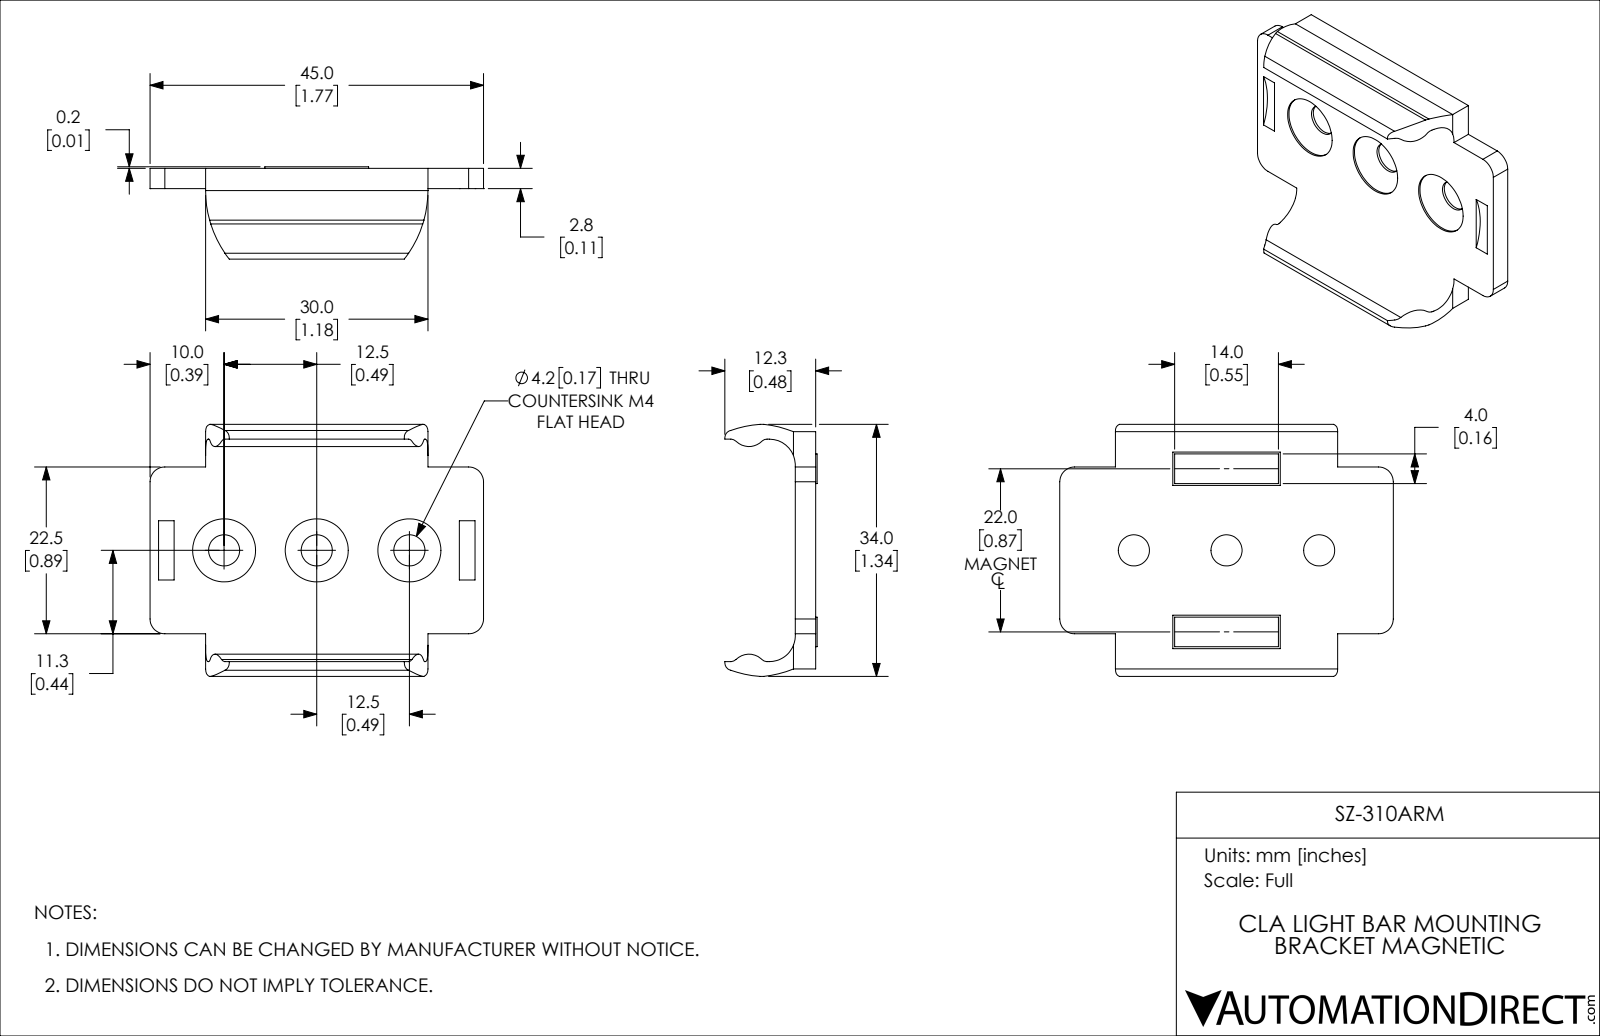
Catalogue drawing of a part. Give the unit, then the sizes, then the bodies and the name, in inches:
Units: inches
Overall size (bounding box): 1.772 × 1.339 × 0.49
Round holes (diameter × count): ⌀0.165 ×3, ⌀0.335 ×3
Partial cylindrical surfaces — rounded edges, fillets, slot ends (radius × count): R0.591 ×5, R0.079 ×4, R0.433 ×1
Main face-to-face distances: 0.866, 0.167, 1.26, 0.157, 0.876, 0.079, 0.315, 0.187, 1.073, 1.033
Hole centre spacings: 0.492, 0.984
Volume: 0.27 in³ · Surface area: 6.795 in²
Bodies: 1 solid, 76 faces (39 planar, 27 cylindrical, 10 other)
Part name (STEP PRODUCT): SZ-310ARM
STEP written by: SolidWorks 2018 (AUTOMOTIVE_DESIGN)
